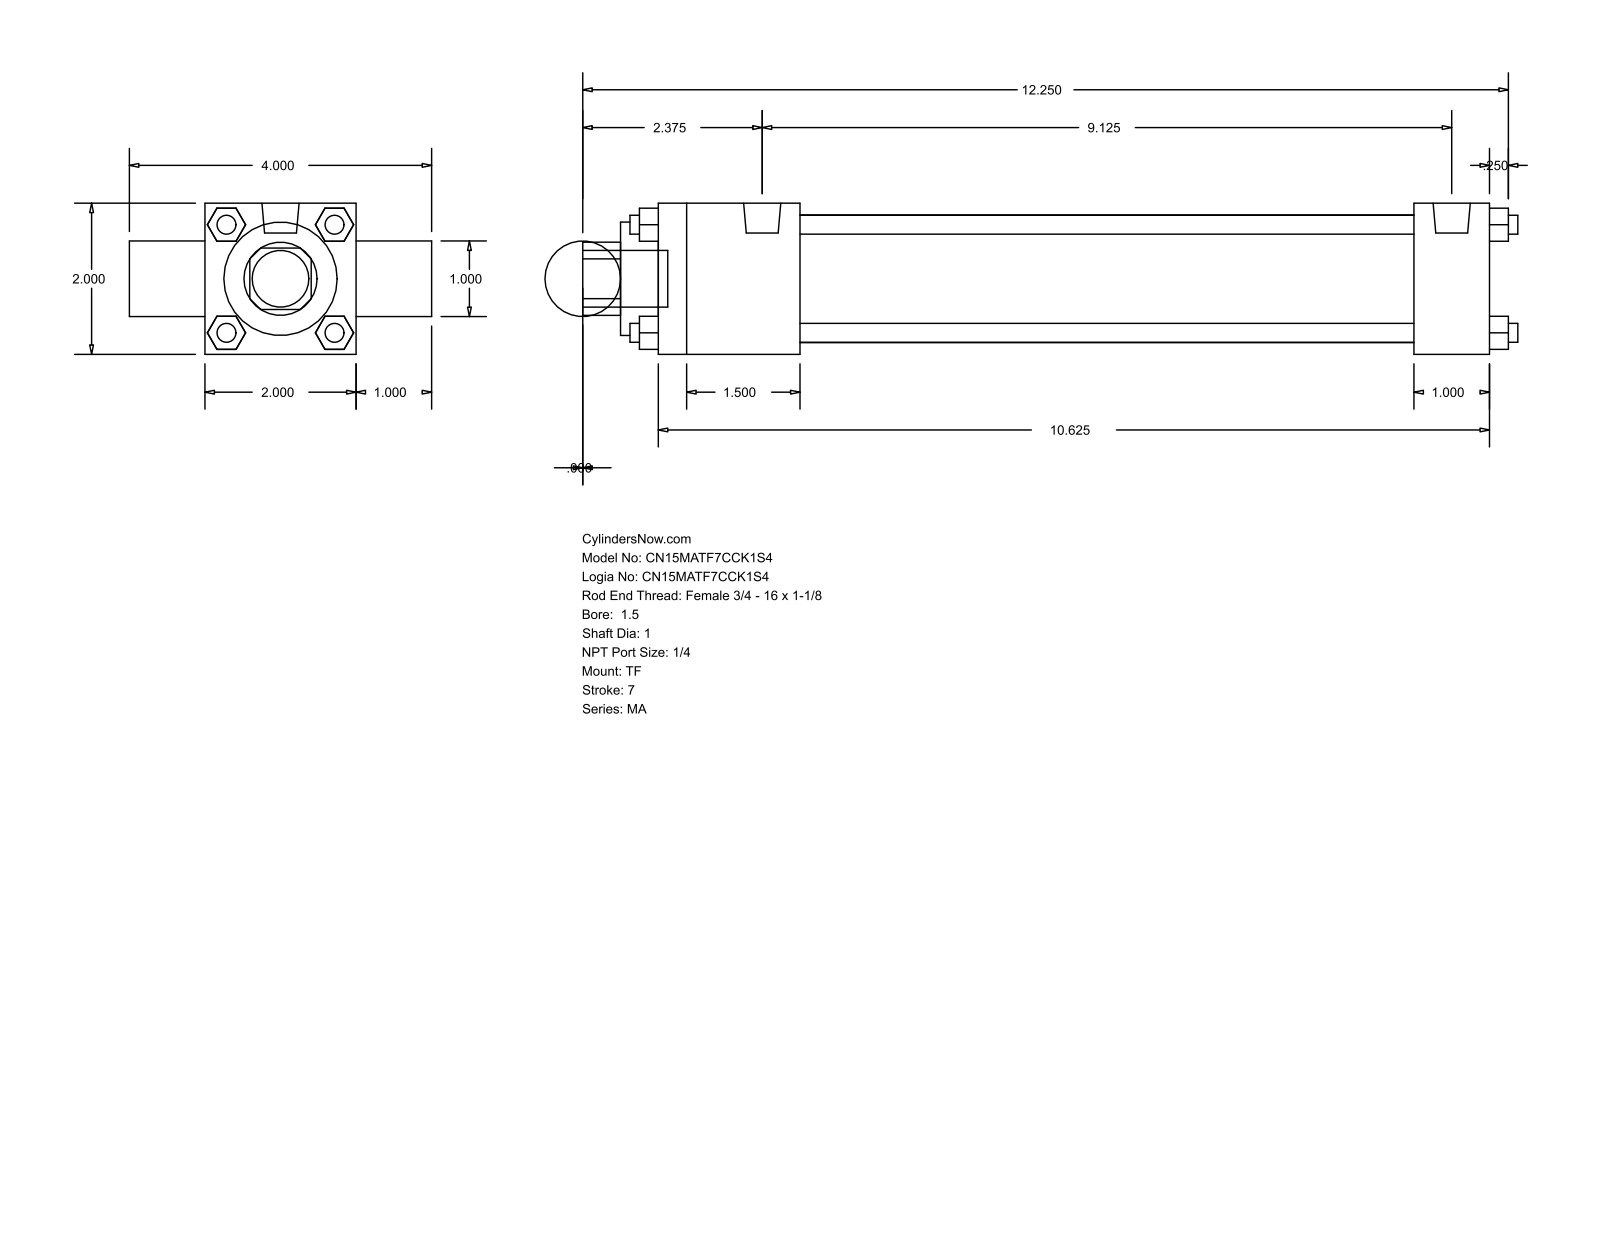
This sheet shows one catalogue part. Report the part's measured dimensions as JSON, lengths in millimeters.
{"part_name": "MA_TF__0150_1", "step_written_by": "GSSL Pune (CONFIG_CONTROL_DESIGN)", "units": "millimeters", "bodies": {"solids": 0, "faces": 120, "planar": 92, "cylindrical": 28, "other": 0}, "overall_size": [314.32, 101.6, 50.8], "round_holes": [[25.4, 2], [38.1, 1], [42.93, 1]], "round_bosses_or_shafts": [[6.35, 4], [7.94, 3], [12.49, 2], [19.05, 1]], "partial_cylinders_radius": [[12.29, 1]], "face_to_face_distances": [50.8, 25.4, 279.4, 76.2, 6.35, 47.63, 254, 206.37, 231.77, 292.1]}
